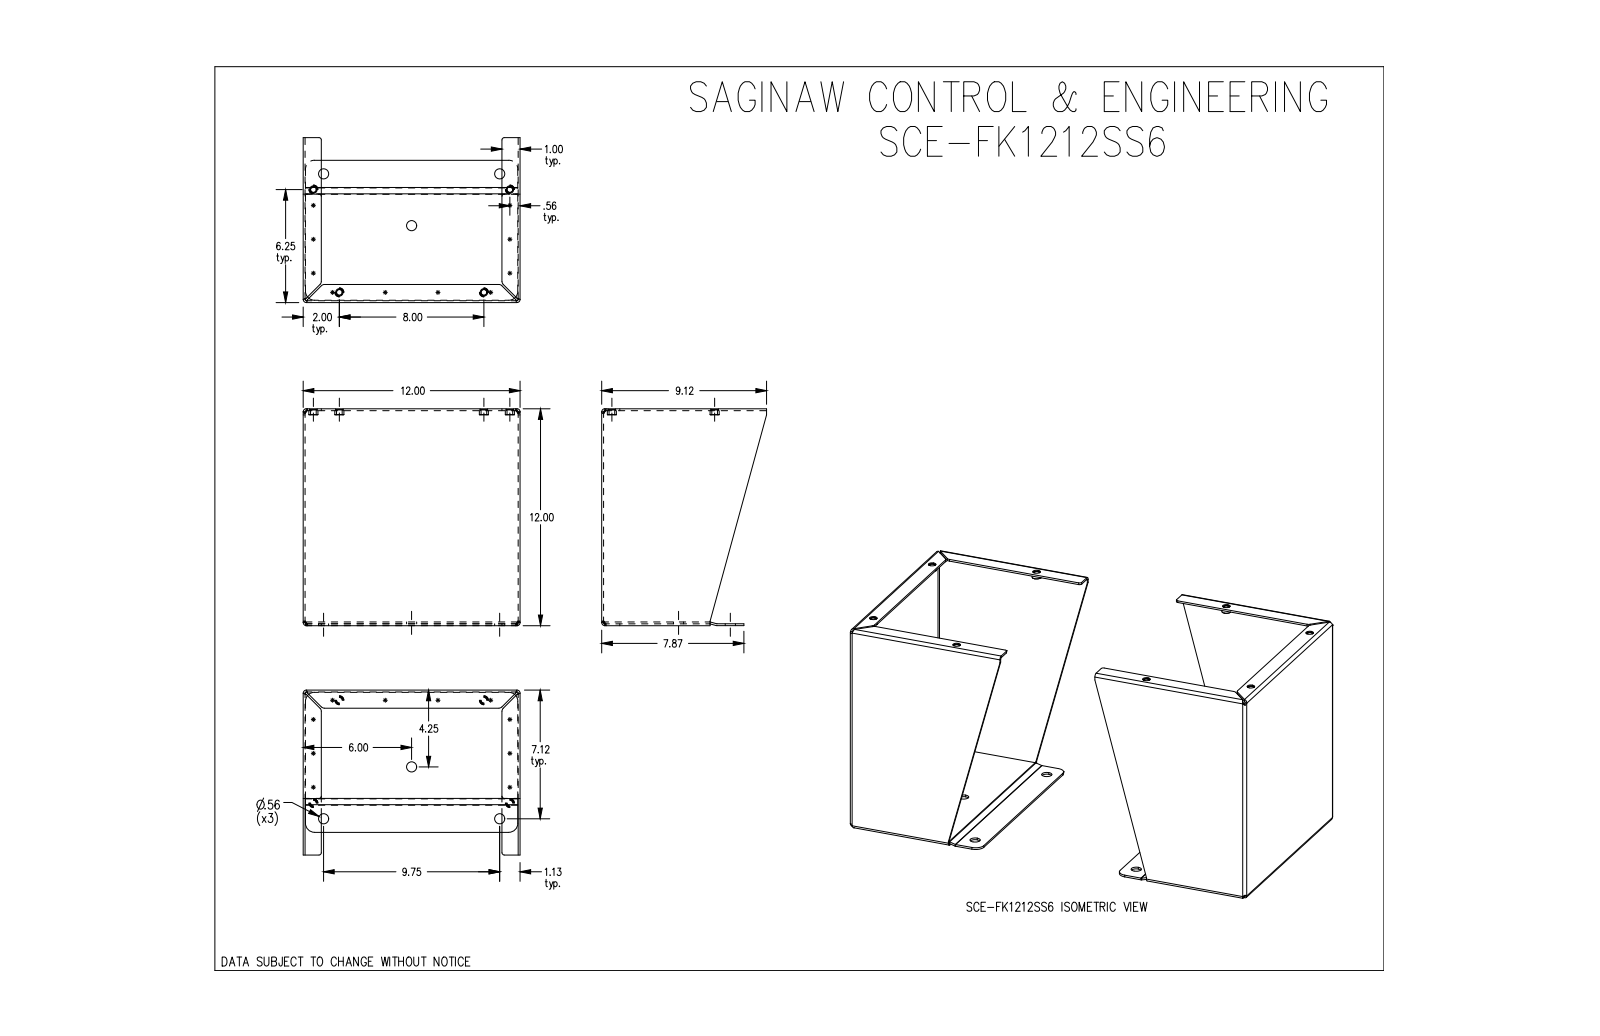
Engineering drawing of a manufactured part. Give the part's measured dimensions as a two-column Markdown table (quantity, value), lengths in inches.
| quantity | value |
| --- | --- |
| part name | SCE-FK1212SS6 |
| STEP written by | SolidWorks 2019 (CONFIG_CONTROL_DESIGN) |
| units | inches |
| bodies | 12 solids, 286 faces (120 planar, 110 cylindrical, 56 other) |
| overall size | 24 × 12 × 12 |
| volume | 94.47 in³ |
| surface area | 1 847 in² |
| round holes (diameter × count) | 0.312 × 8, 0.413 × 8, 0.563 × 6 |
| round bosses / shafts (diameter × count) | 0.5 × 8, 0.412 × 8 |
| partial cylindrical surfaces (radius × count) | 0.166 × 16, 0.062 × 12, 0.125 × 8, 0.22 × 8, 0.5 × 8, 0.063 × 4 |
| main face-to-face distances | 0.104, 11.896, 23.896, 11.792, 12, 24, 23.792, 0.101, 11.893, 11.688 |
| hole center spacings | 1.035, 5.441, 5.656, 5.793, 5.866, 6.614, 10.646, 11.019 |
